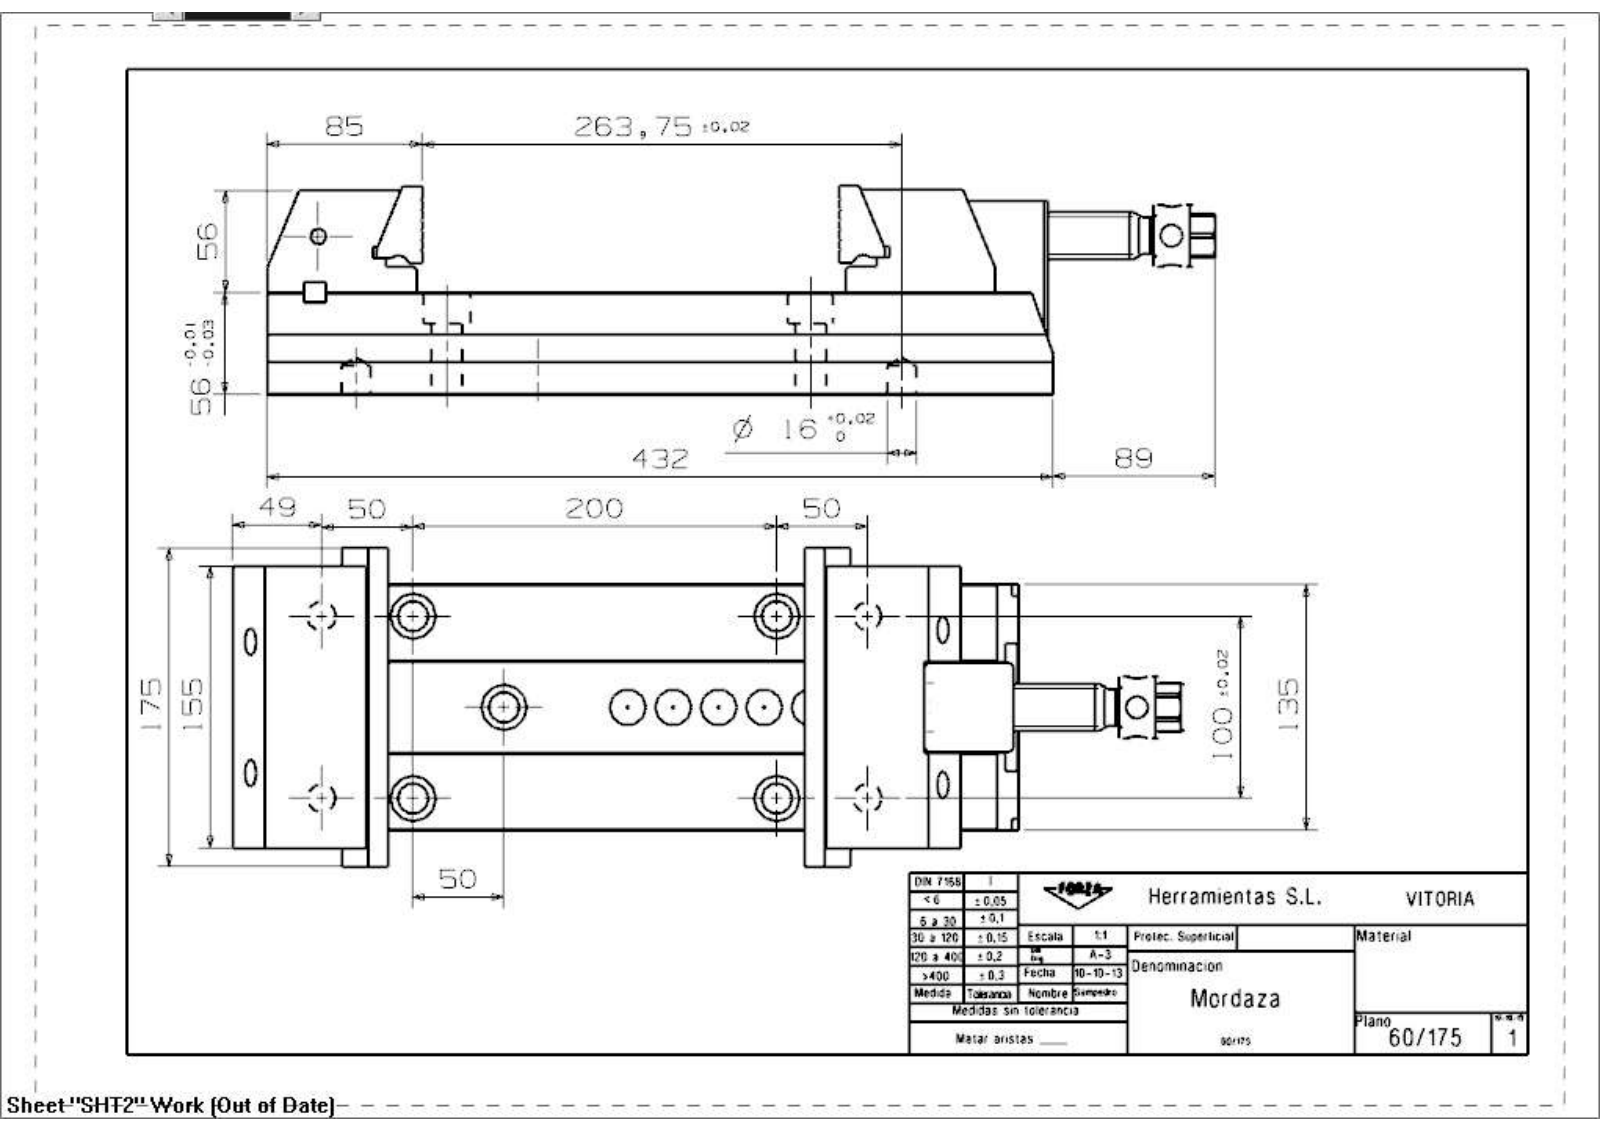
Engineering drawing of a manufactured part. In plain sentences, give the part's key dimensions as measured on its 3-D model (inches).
The part is named "15090 Montaje taco atras; 60_175_Mordaza". Its 3-D file was written by "SIEMENS PLM Software NX 7.5 (CONFIG_CONTROL_DESIGN)". It is 12 solids with 447 faces: 287 planar, 97 cylindrical and 63 other. Overall it measures 20.512 by 6.89 by 4.512 inches. Its volume is 228.5 cubic inches and its surface area 784.3 square inches. Round holes: 6 of diameter 0.591, 5 of diameter 0.346, 5 of diameter 0.63, 5 of diameter 0.669, 5 of diameter 0.984, 4 of diameter 0.275, 4 of diameter 0.335, 4 of diameter 0.394, 4 of diameter 0.417, 4 of diameter 0.512, 4 of diameter 0.748, 2 of diameter 0.472. Round bosses or shafts: 1 of diameter 1.339, 1 of diameter 1.331, 1 of diameter 1.024, 1 of diameter 0.787, 1 of diameter 0.65. Partial cylindrical surfaces (rounded edges, fillets, slot ends): 4 of radius 0.787, 2 of radius 0.063, 2 of radius 0.236, 2 of radius 0.276, 1 of radius 0.157, 1 of radius 0.354, 1 of radius 0.413, 1 of radius 0.492. The main face-to-face distances are 2.205, 1.252, 0.953, 0.394, 4.035, 1.673, 4.429, 5.315, 1.28, 2.067. The hole center spacings are 3.091, 3.937, 4.402, 0.256, 0.256, 1.969, 2.835, 3.346.
